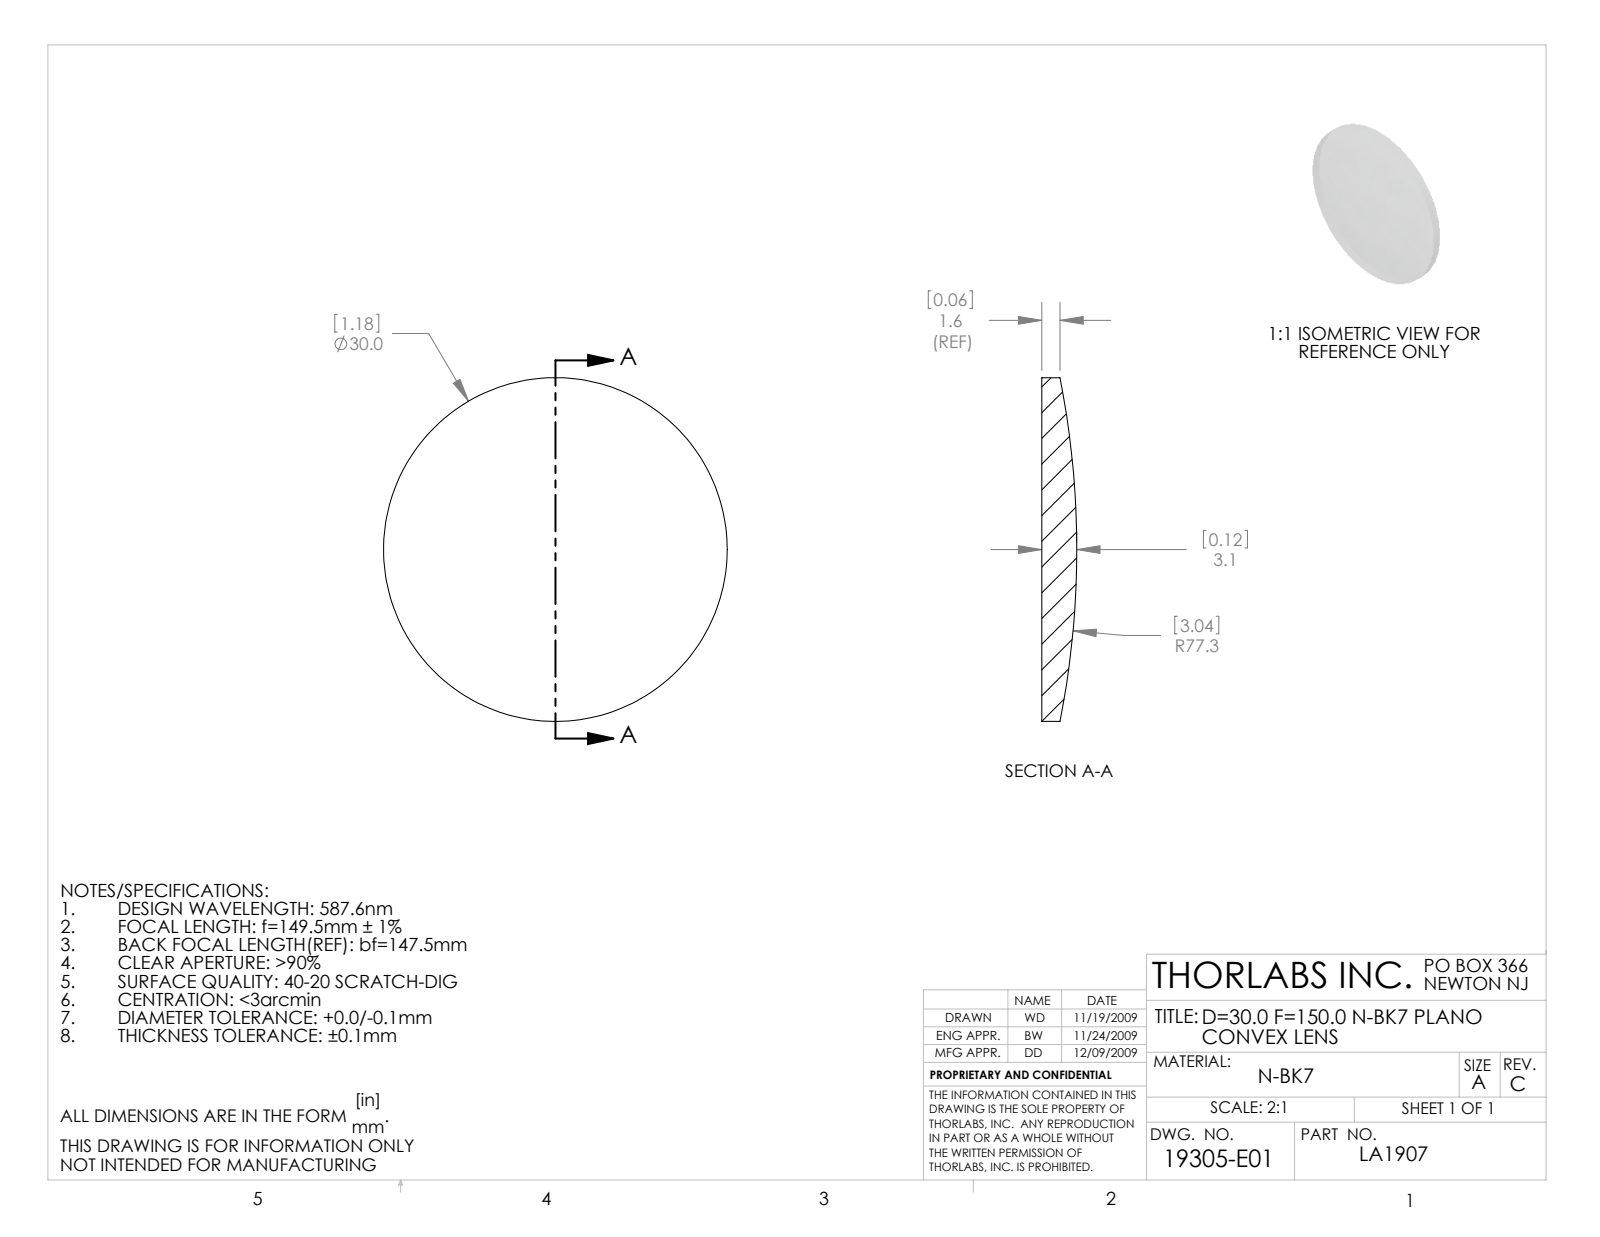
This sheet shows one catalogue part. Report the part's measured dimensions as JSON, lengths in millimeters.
{"part_name": "19305-E0W", "step_written_by": "SolidWorks 2009 (AUTOMOTIVE_DESIGN)", "units": "millimeters", "bodies": {"solids": 1, "faces": 5, "planar": 1, "cylindrical": 2, "other": 2}, "overall_size": [30, 30, 3.05], "volume_mm3": 1638, "surface_area_mm2": 1569, "round_bosses_or_shafts": [[30, 1]]}
